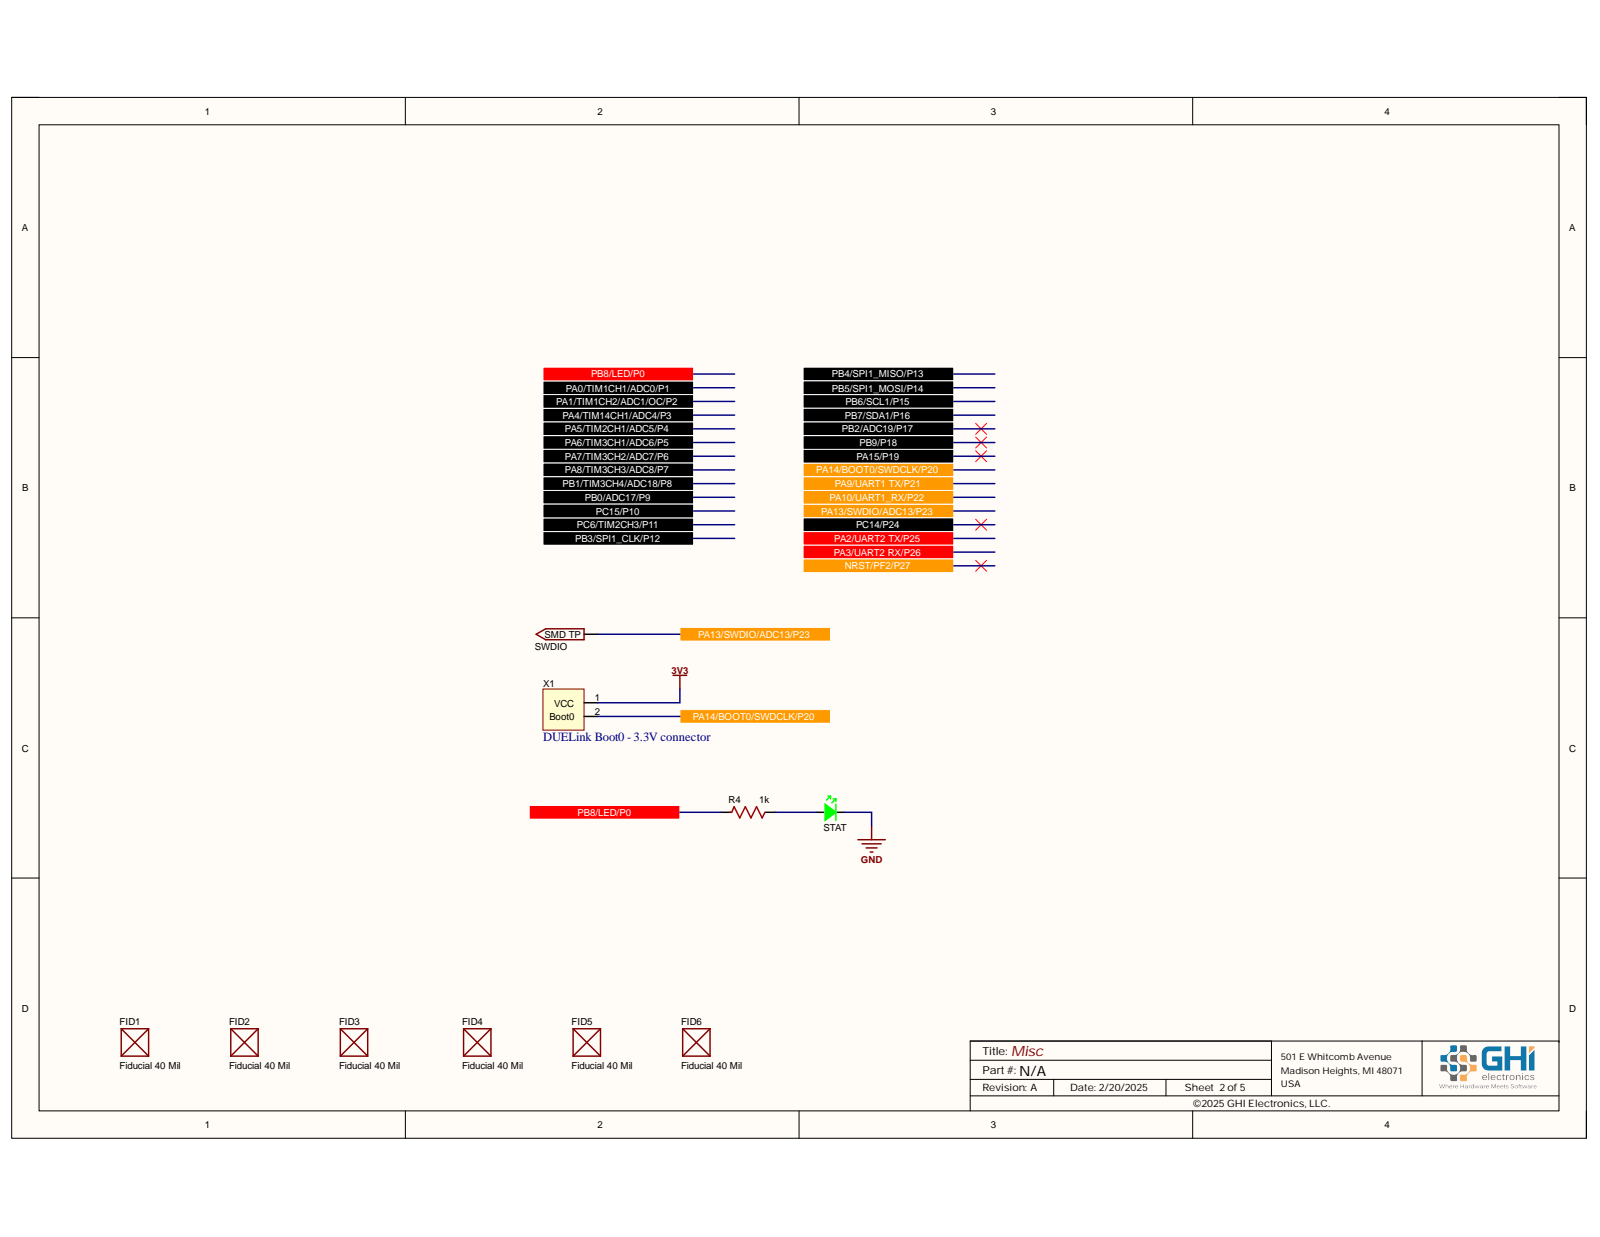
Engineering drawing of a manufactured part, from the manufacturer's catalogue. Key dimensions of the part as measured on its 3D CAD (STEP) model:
Part name (STEP PRODUCT): PCB; Board; 61302021821; 6130xx21821_PIN (+5 more)
STEP written by: Open CASCADE 7.5 (AUTOMOTIVE_DESIGN)
Units: millimetres
Bodies: 133 solids, 3150 faces (2324 planar, 558 cylindrical, 268 other)
Overall size (bounding box): 187.78 × 90.17 × 17.08
Volume: 109 657 mm³ · Surface area: 78 614 mm²
Round holes (diameter × count): ⌀3.3 ×48, ⌀1.02 ×20, ⌀3.17 ×4, ⌀1.02 ×2, ⌀3 ×2
Partial cylindrical surfaces — rounded edges, fillets, slot ends (radius × count): R0.51 ×104, R0.12 ×35, R0.58 ×20, R0.15 ×14, R3.17 ×4, R0.17 ×2, R0.18 ×2, R0.18 ×2
Main face-to-face distances: 1.78, 16.71, 50.14, 17.08, 15.3, 15.5, 33.43, 19.1, 45.67, 66.85
Hole centre spacings: 2.54, 3.59, 5.08, 5.68, 7.62, 8.03, 10.16, 10.47
